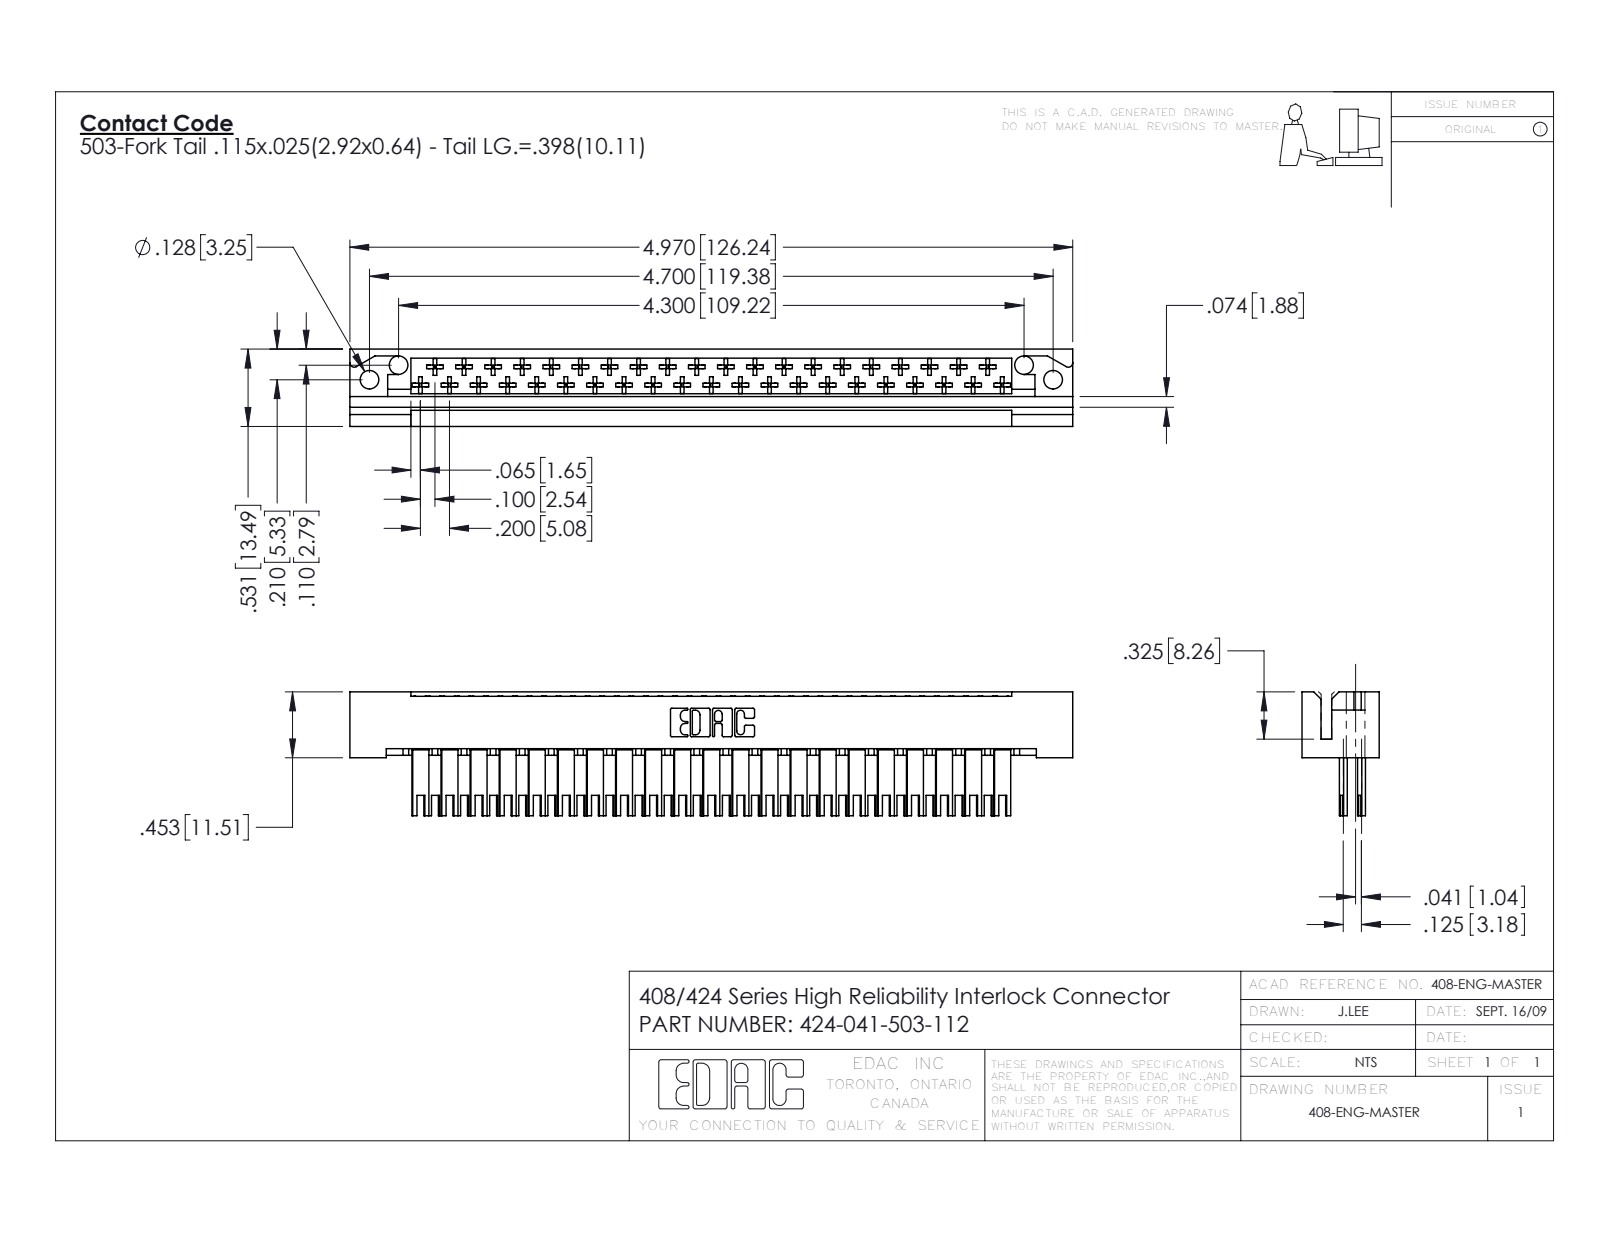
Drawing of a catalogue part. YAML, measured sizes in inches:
part_name: "408-290-001_408-290-103; 424 Part_041; 424-047-503-112"
step_written_by: "SolidWorks 2016 (CONFIG_CONTROL_DESIGN)"
units: inches
bodies: {solids: 42, faces: 2318, planar: 1770, cylindrical: 384, other: 164}
overall_size: [4.97, 0.851, 0.531]
volume: 0.876
surface_area: 29.96
round_holes:
  - {diameter: 0.128, count: 4}
partial_cylinders:
  - {radius: 0.01, count: 246}
  - {radius: 0.02, count: 43}
  - {radius: 0.01, count: 22}
  - {radius: 0.007, count: 6}
  - {radius: 0.031, count: 6}
  - {radius: 0.026, count: 3}
  - {radius: 0.03, count: 2}
face_to_face_distances: [0.025, 0.531, 0.125, 0.4, 0.1, 0.235, 0.259, 0.272, 0.025, 0.296]
hole_center_spacings: [0.224, 4.501, 4.3, 4.7]
